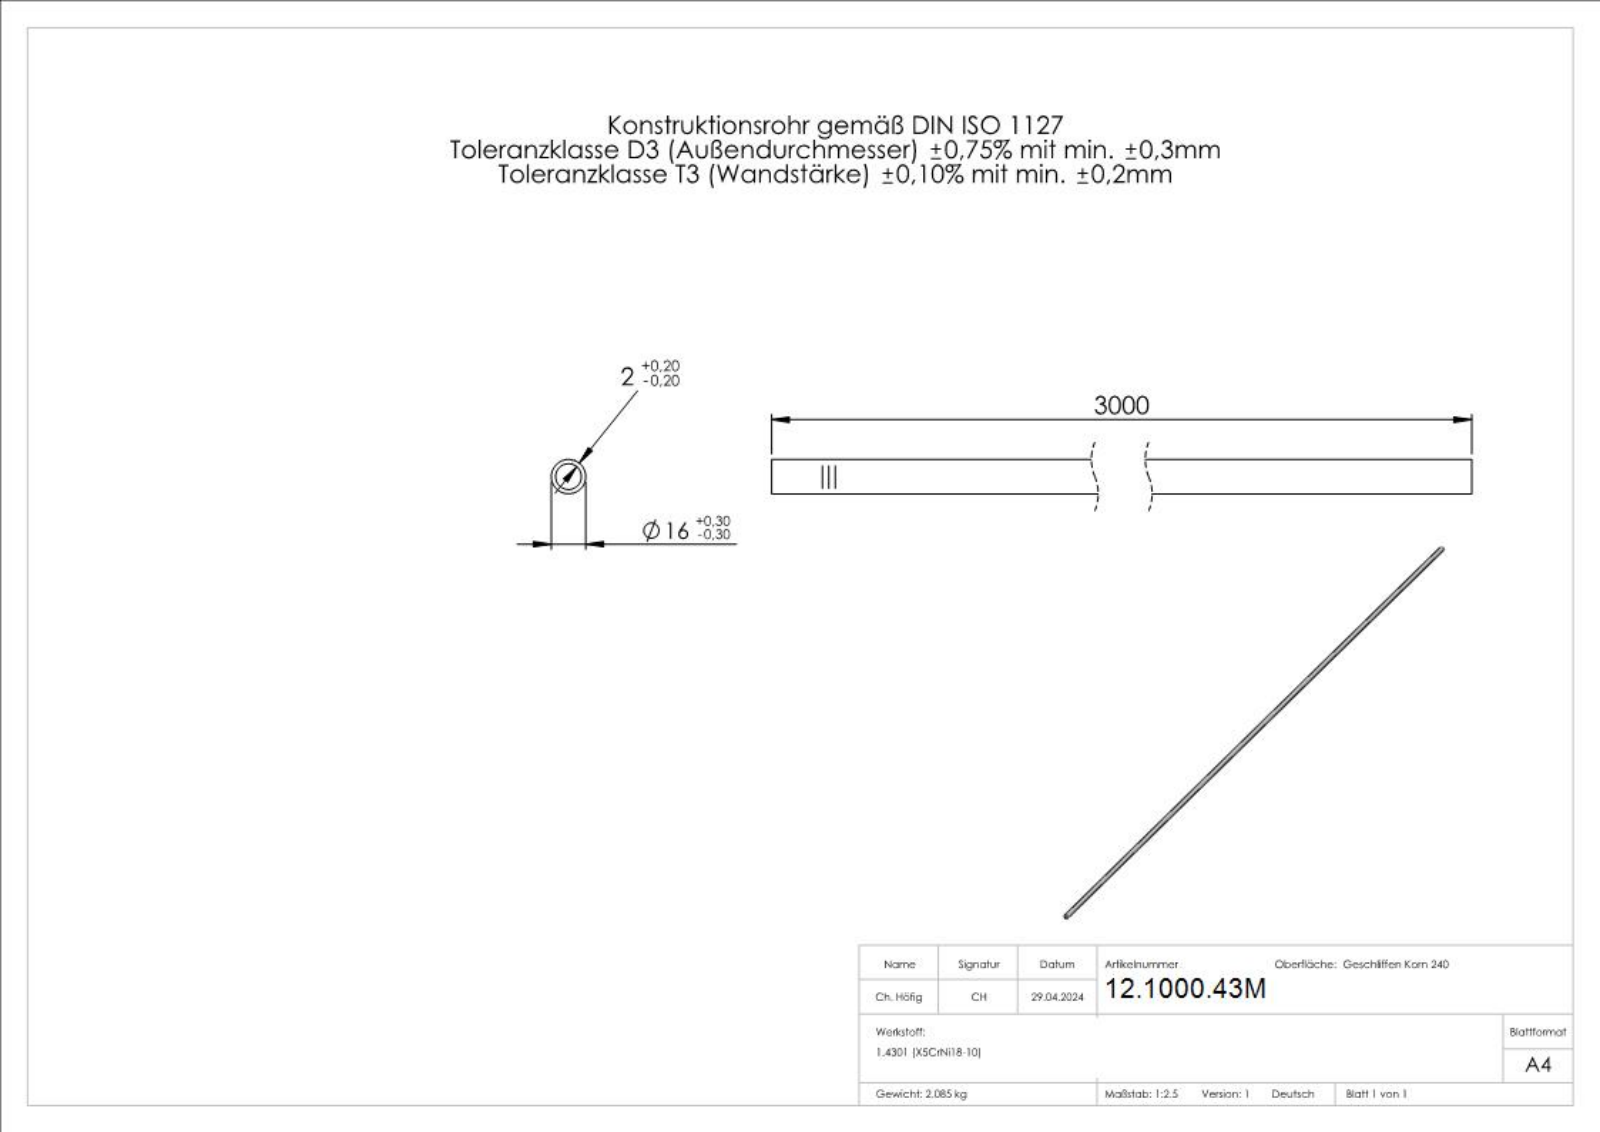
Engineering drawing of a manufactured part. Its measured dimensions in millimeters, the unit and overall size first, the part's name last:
Units: millimetres
Overall size (bounding box): 3000 × 16 × 16
Round holes (diameter × count): ⌀12 ×1
Round bosses / shafts (diameter × count): ⌀16 ×1
Partial cylindrical surfaces — rounded edges, fillets, slot ends (radius × count): R6.1 ×1
Main face-to-face distances: 3000, 1.57, 2.41, 0.73, 2.24, 2.61, 0.79, 1.21, 2.45, 0.47
Volume: 263 893 mm³ · Surface area: 264 078 mm²
Bodies: 1 solid, 305 faces (135 planar, 30 cylindrical, 140 other)
Part name (STEP PRODUCT): 55099-2403M
STEP written by: SolidWorks 2018 (CONFIG_CONTROL_DESIGN)
